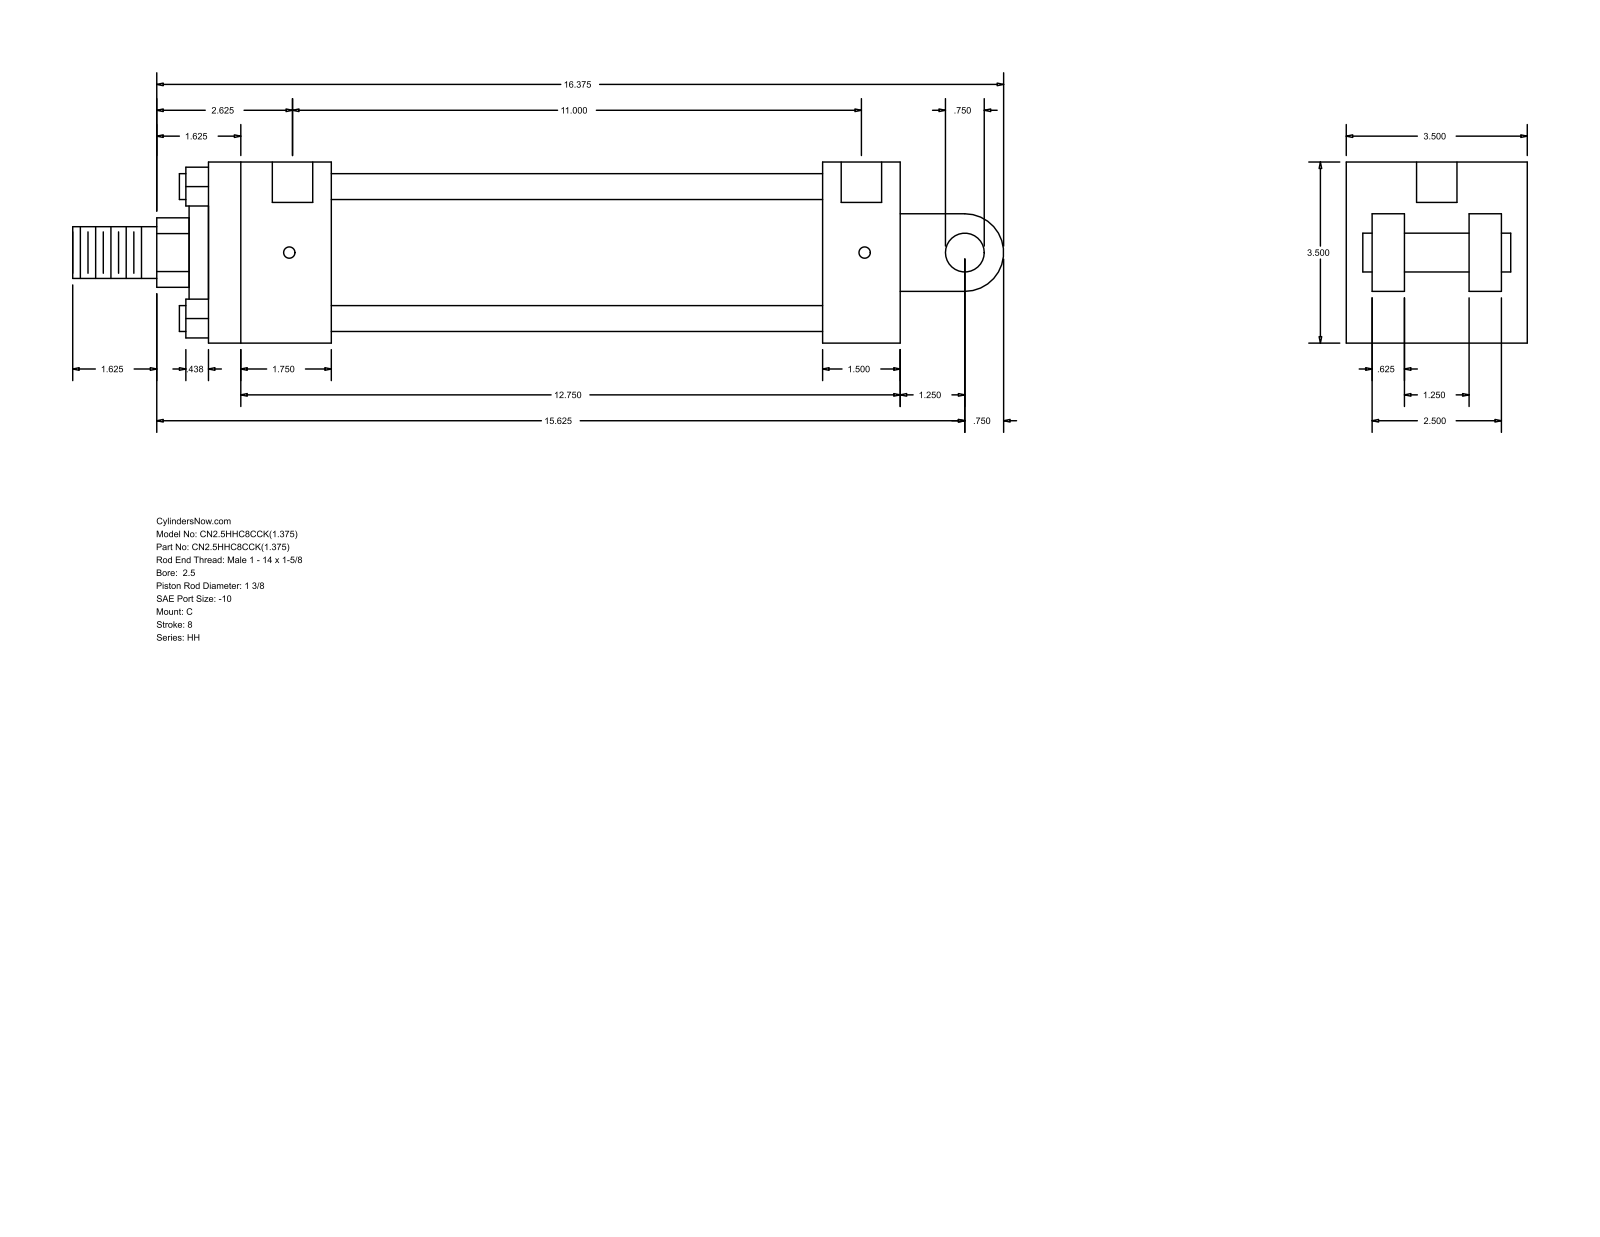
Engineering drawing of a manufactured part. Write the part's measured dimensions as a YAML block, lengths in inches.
part_name: "HH_C__0250_1.375"
step_written_by: "GSSL Pune (CONFIG_CONTROL_DESIGN)"
units: inches
bodies: {solids: 0, faces: 99, planar: 70, cylindrical: 29, other: 0}
overall_size: [18, 3.5, 3.5]
round_holes:
  - {diameter: 0.219, count: 4}
  - {diameter: 0.781, count: 2}
round_bosses_or_shafts:
  - {diameter: 0.5, count: 4}
  - {diameter: 2.875, count: 1}
  - {diameter: 2, count: 1}
  - {diameter: 1.375, count: 1}
  - {diameter: 1, count: 1}
  - {diameter: 0.75, count: 1}
partial_cylinders:
  - {radius: 0.672, count: 1}
  - {radius: 0.75, count: 1}
face_to_face_distances: [3.5, 13.375, 1.5, 2.5, 0.5, 11.875, 2.375, 9.5, 11, 3]
hole_center_spacings: [11.125, 0.062, 0.063, 11, 11.062, 11.063]
